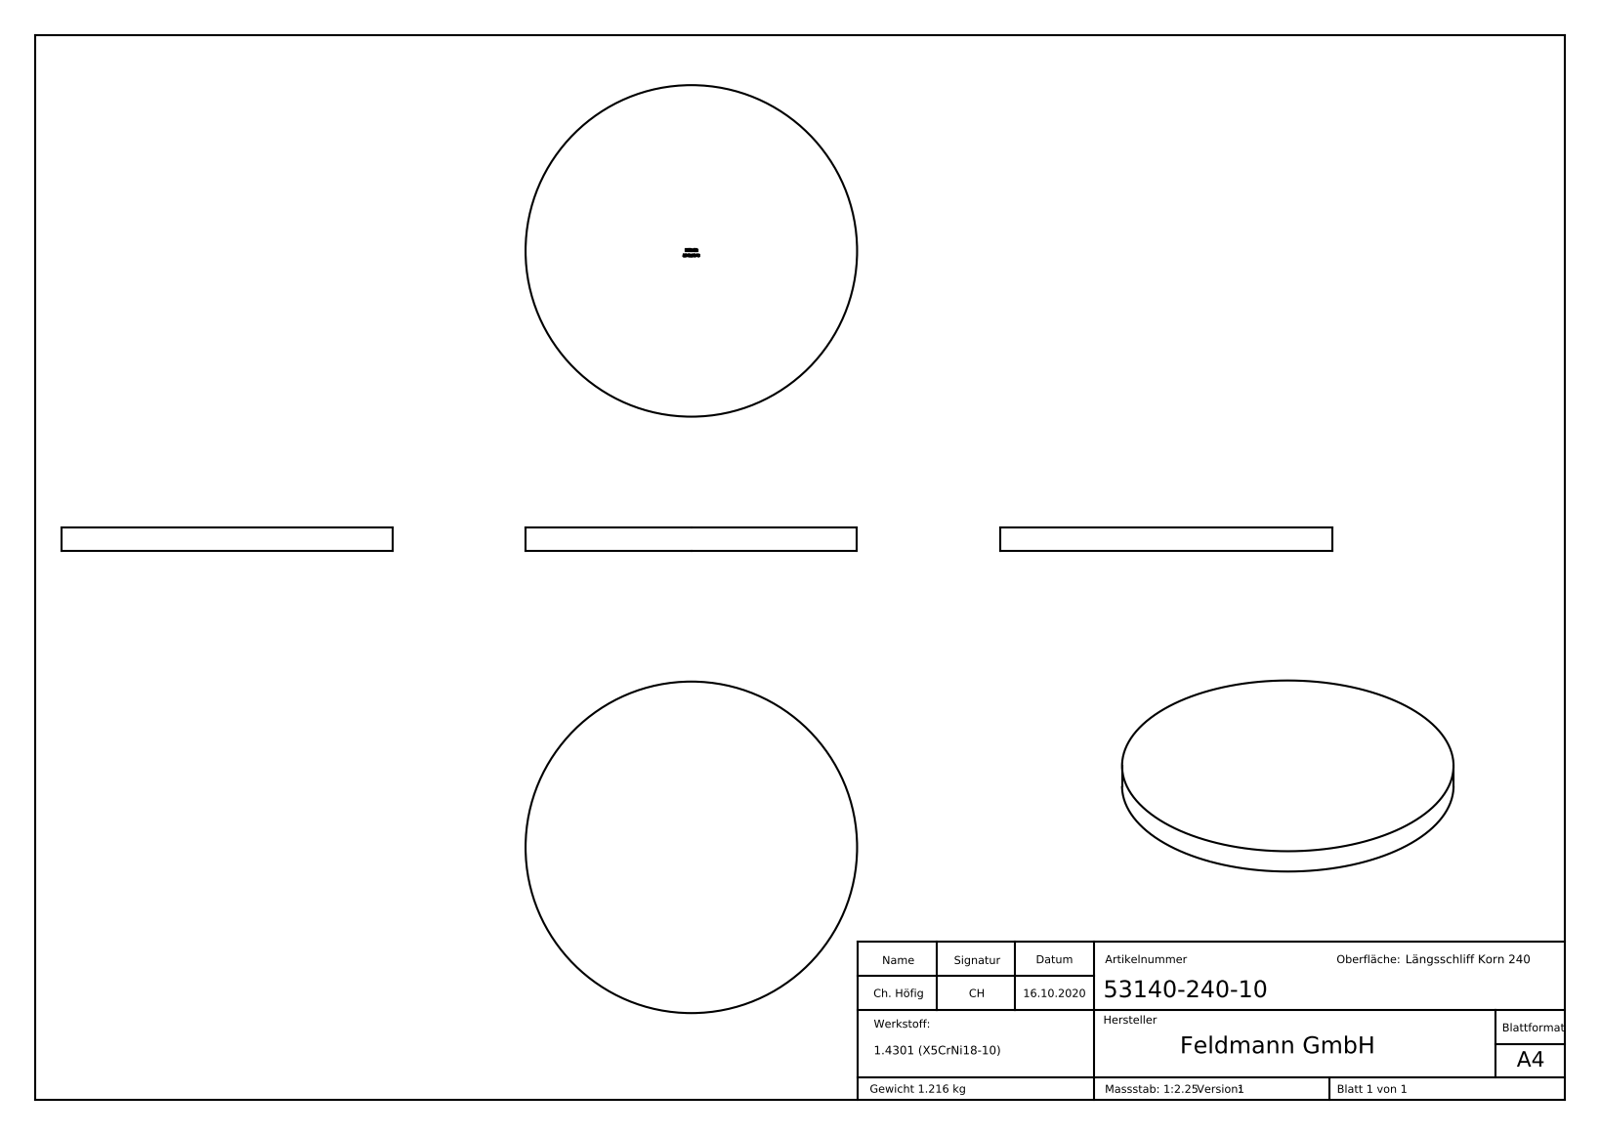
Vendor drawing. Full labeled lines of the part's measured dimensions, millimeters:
Part name (STEP PRODUCT): 53140-240-10
STEP written by: SolidWorks 2018 (CONFIG_CONTROL_DESIGN)
Units: millimetres
Bodies: 1 solid, 250 faces (145 planar, 2 cylindrical, 103 other)
Overall size (bounding box): 140 × 140 × 10
Volume: 153 938 mm³ · Surface area: 35 192 mm²
Round bosses / shafts (diameter × count): ⌀140 ×1
Main face-to-face distances: 10, 9.9, 1.39, 2.2, 2.45, 0.65, 0.74, 0.99, 1.55, 0.81
